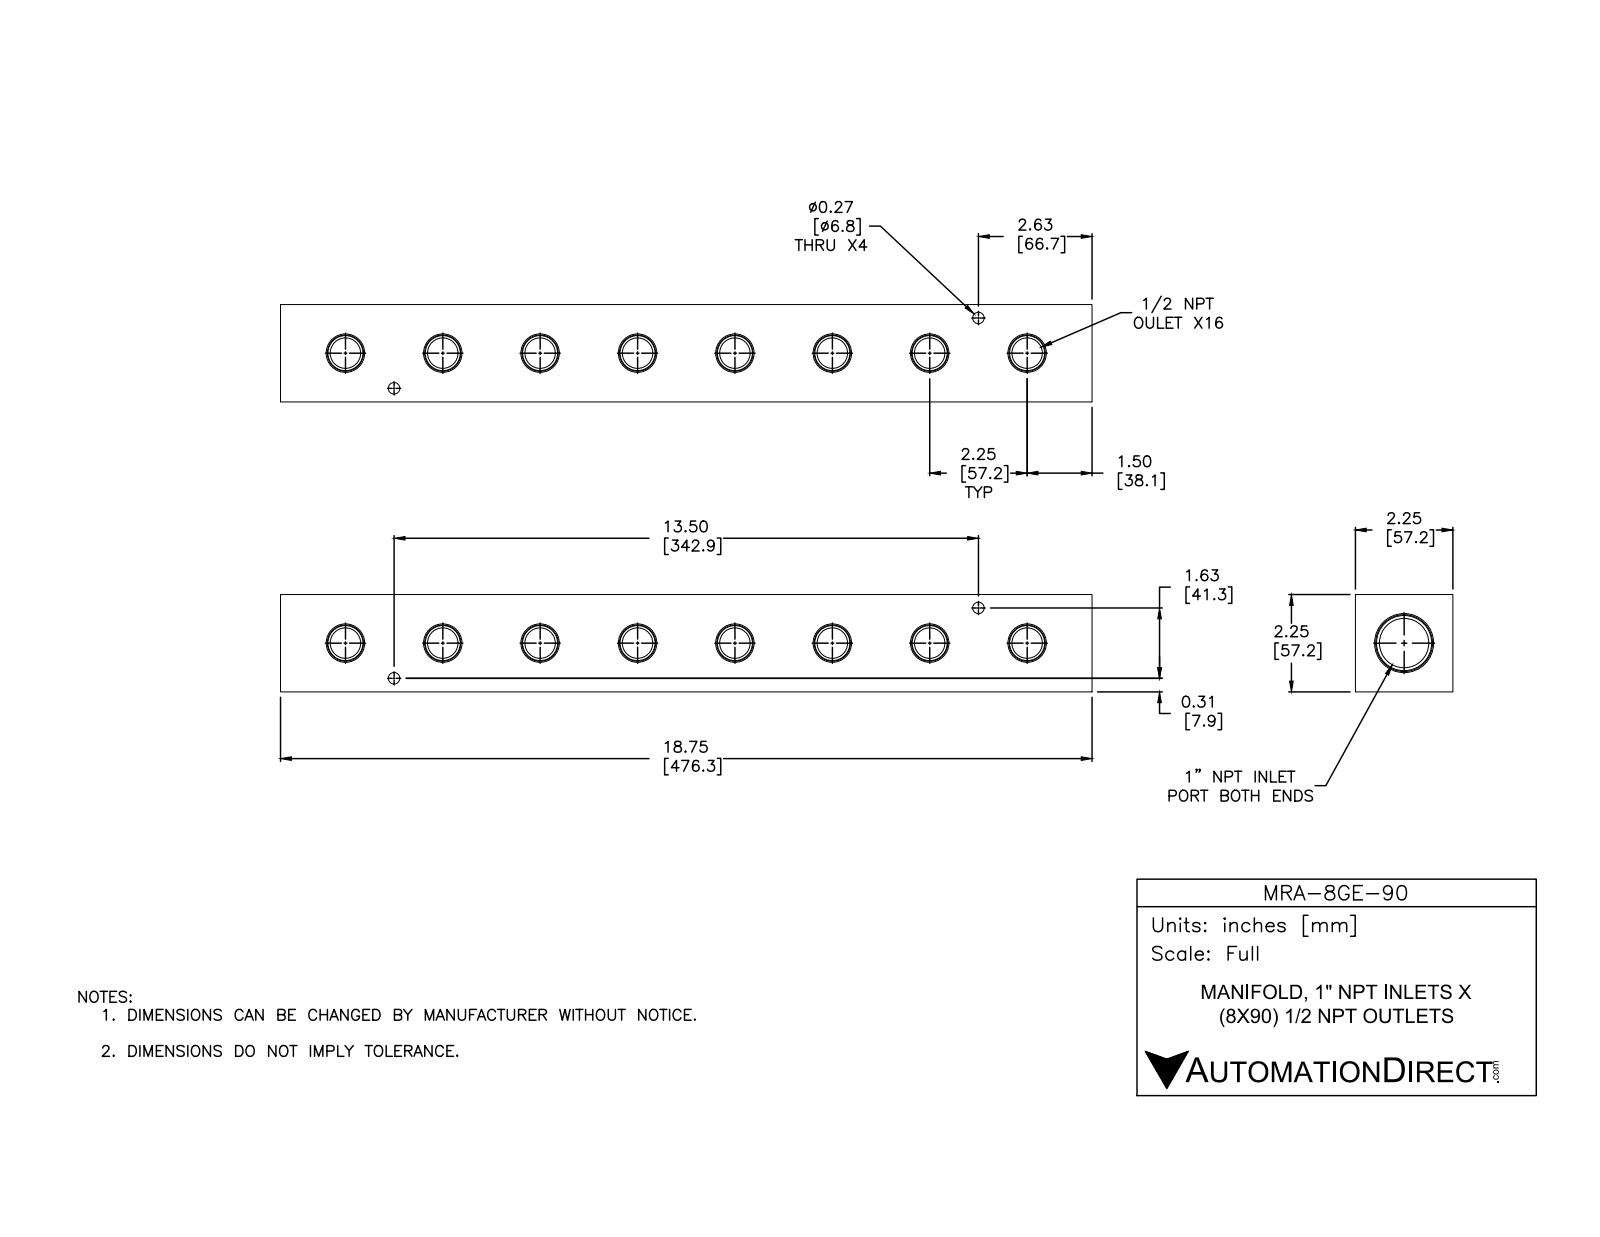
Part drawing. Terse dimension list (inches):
name: MRA-8GE-90
written by: SolidWorks 2015 (CONFIG_CONTROL_DESIGN)
unit: in
bodies: 1 solid, 146 faces (24 planar, 50 cylindrical, 72 other)
size: 18.75 × 2.25 × 2.25
volume: 70 in³; area: 261.9 in²
holes: 16× ⌀0.703, 4× ⌀0.266, 1× ⌀1.141
face distances: 2.25, 18.75, 0.53, 1.72, 0.66, 18.09, 17.43
hole spacings: 2.25, 4.5, 1.388, 6.75, 9, 11.25, 14.648, 2.25
